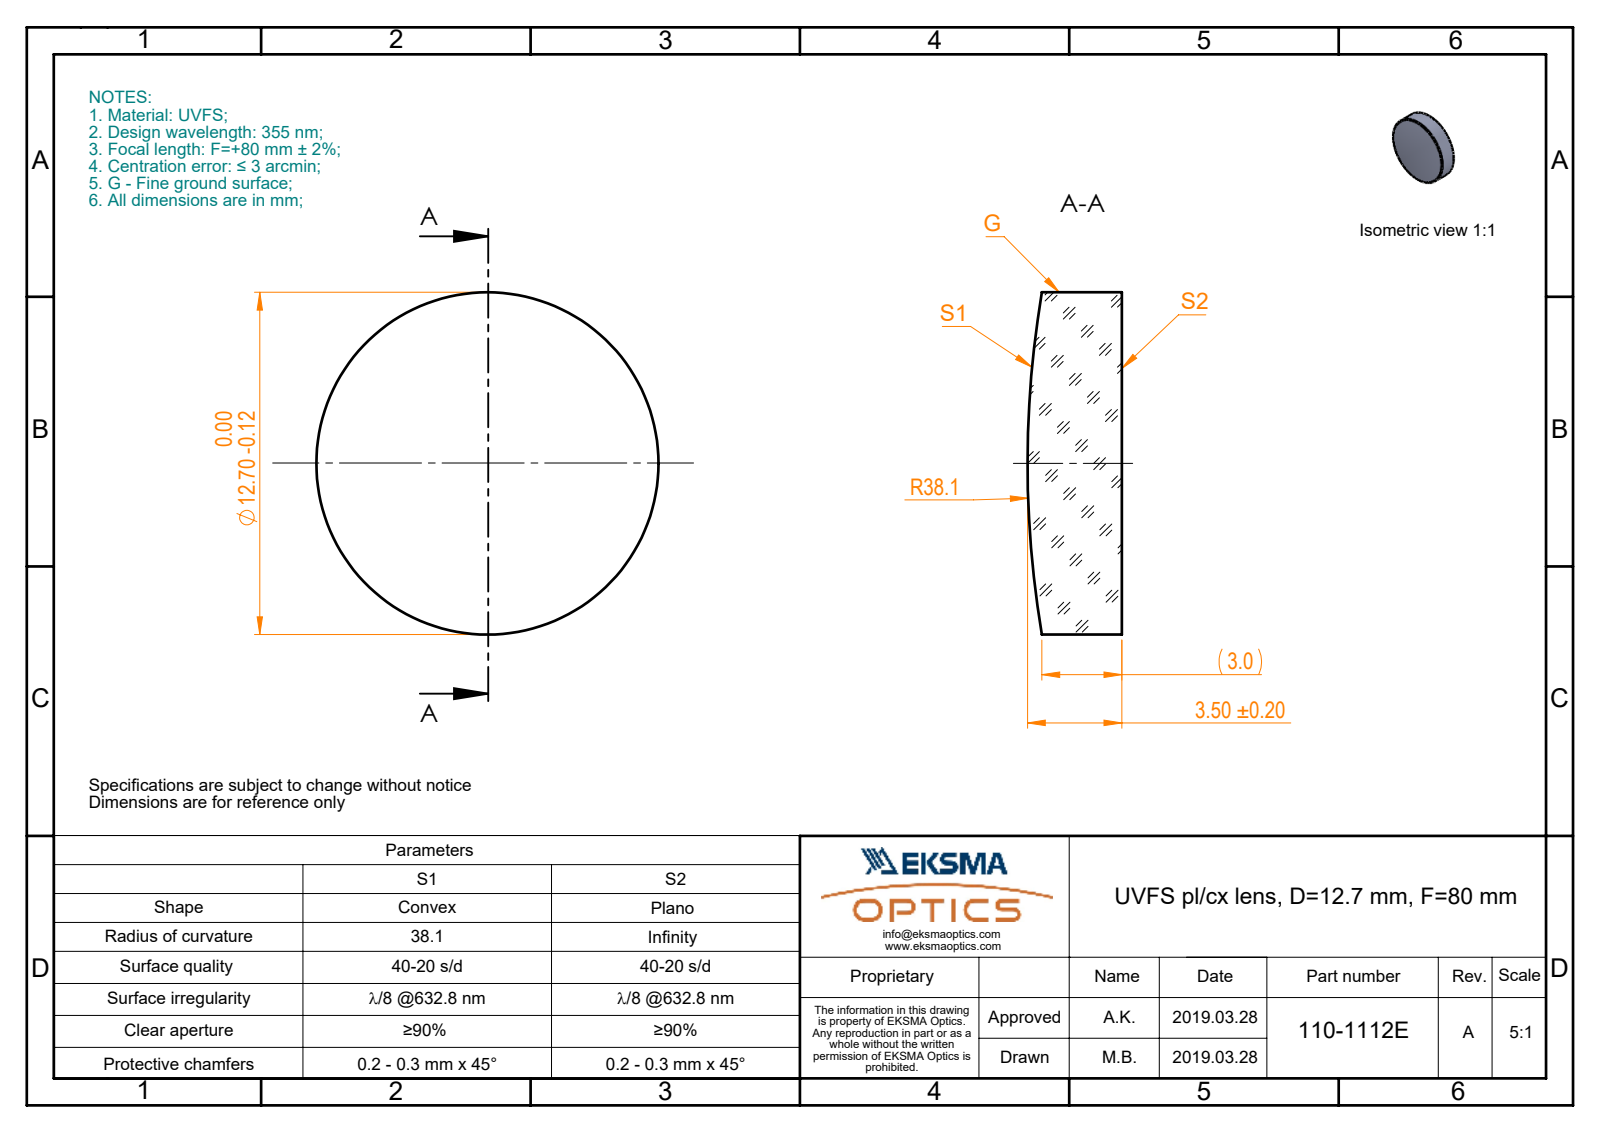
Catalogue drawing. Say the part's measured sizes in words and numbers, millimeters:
The part is named "110-1112E UVFS pl-cx 12.7 F80". Its 3-D file was written by "SolidWorks 2017 (CONFIG_CONTROL_DESIGN)". It is 1 solid with 5 faces: 1 planar, 2 cylindrical and 2 other. Overall it measures 12.7 by 12.7 by 3.5 millimeters. Its volume is 410 cubic millimeters and its surface area 373 square millimeters. Round bosses or shafts: 1 of diameter 12.7.
